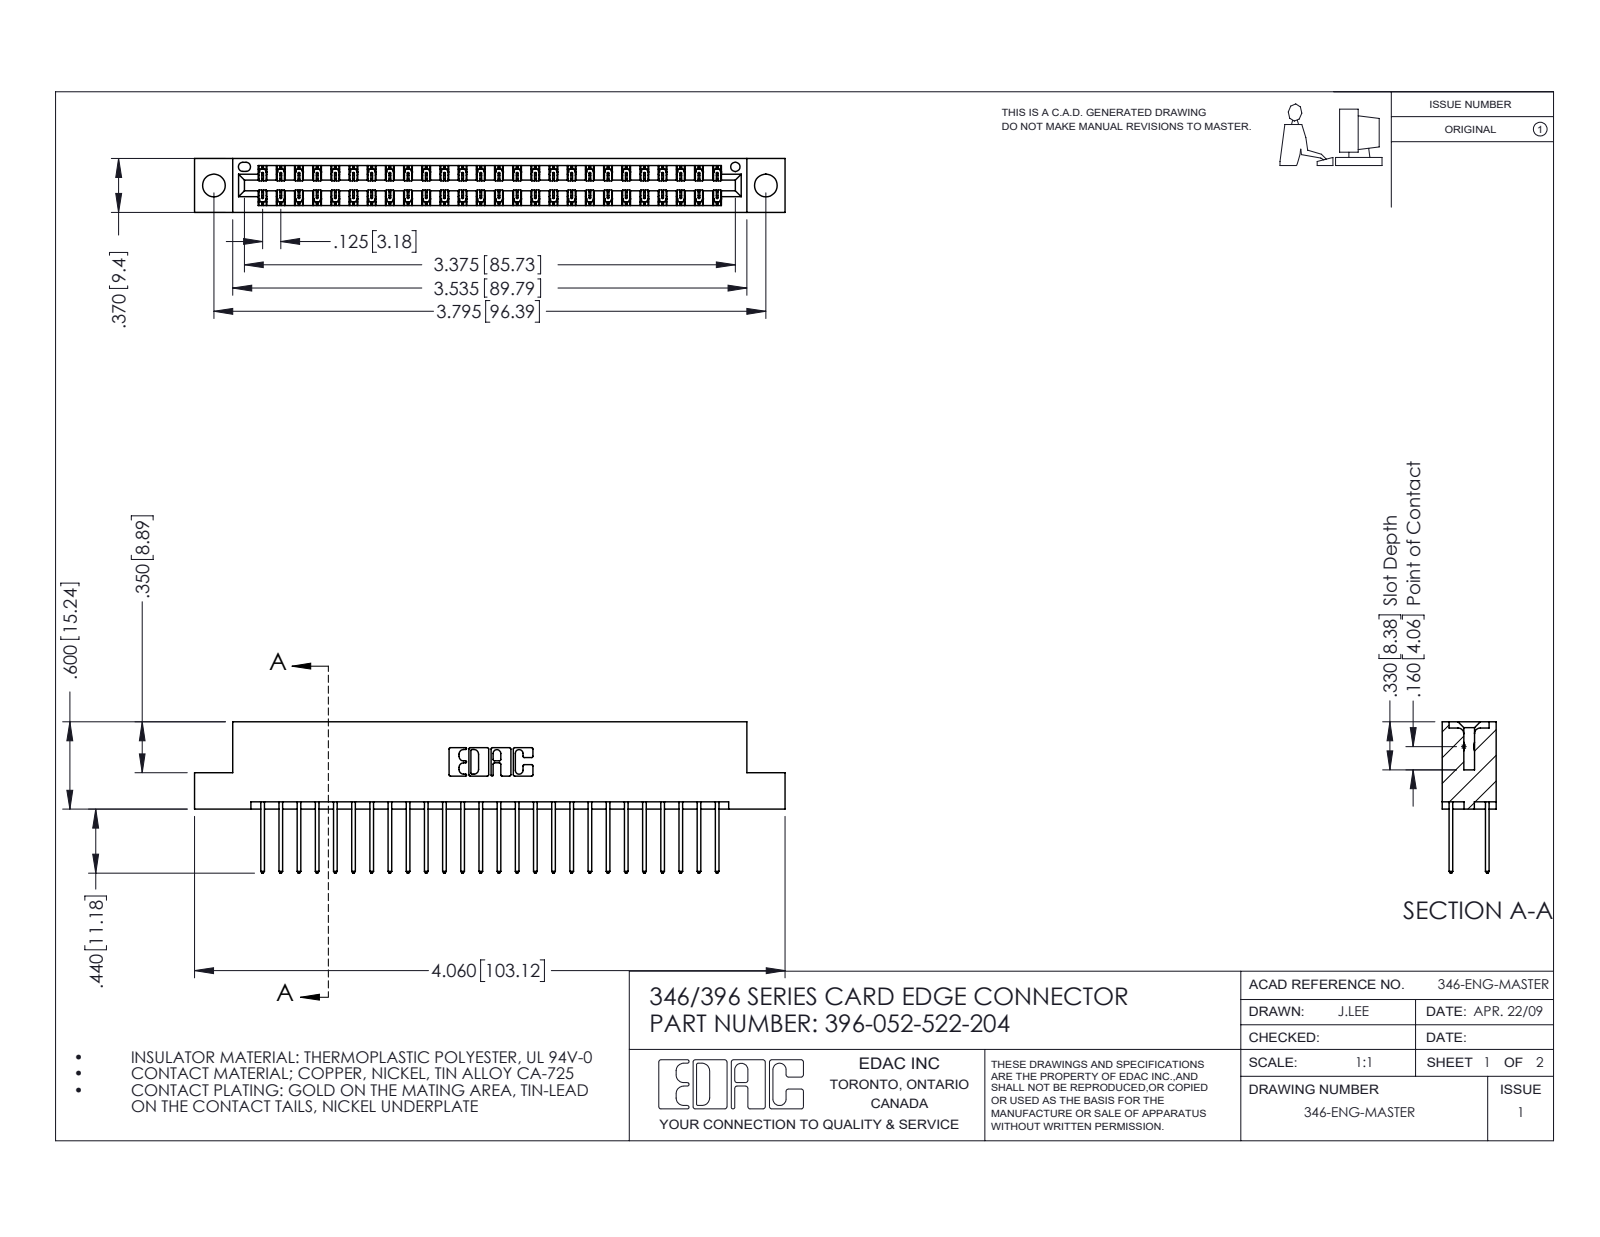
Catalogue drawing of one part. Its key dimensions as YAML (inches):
part_name: "346 Part_Flush Mounting Lugs - 0.156 Dia-TH; 396-052-522-204; 345-292-001_345-293-122"
step_written_by: "SolidWorks 2016 (CONFIG_CONTROL_DESIGN)"
units: inches
bodies: {solids: 53, faces: 2826, planar: 1896, cylindrical: 930, other: 0}
overall_size: [4.06, 1.04, 0.37]
volume: 0.609
surface_area: 21.54
round_holes:
  - {diameter: 0.156, count: 2}
  - {diameter: 0.064, count: 1}
partial_cylinders:
  - {radius: 0.006, count: 78}
  - {radius: 0.01, count: 52}
  - {radius: 0.01, count: 22}
  - {radius: 0.007, count: 6}
  - {radius: 0.031, count: 6}
  - {radius: 0.026, count: 3}
  - {radius: 0.014, count: 2}
  - {radius: 0.022, count: 2}
face_to_face_distances: [0.048, 0.322, 0.25, 0.37, 0.072, 0.298, 0.025, 0.275, 0.148, 0.222]
hole_center_spacings: [0.246, 3.587, 3.795]
